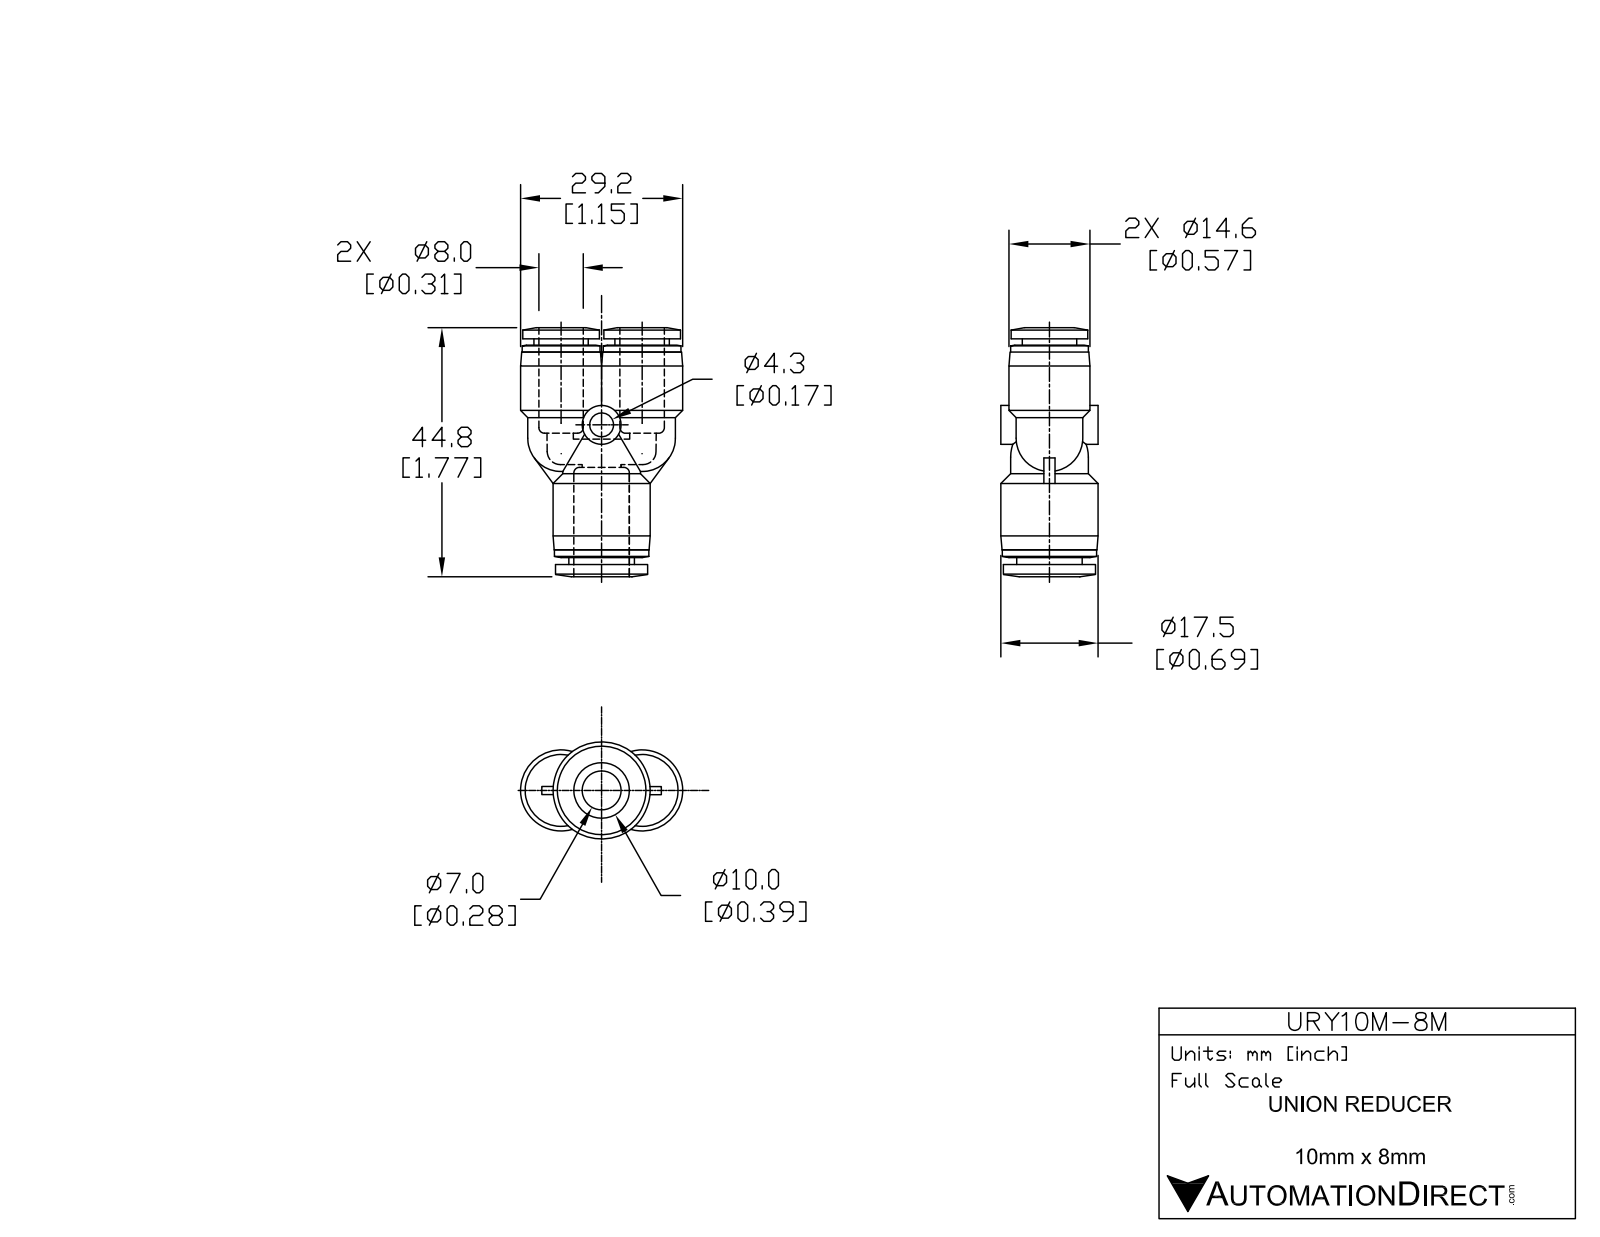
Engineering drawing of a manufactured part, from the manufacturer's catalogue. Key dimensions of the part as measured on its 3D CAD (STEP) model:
Part name (STEP PRODUCT): URY10M-8M
STEP written by: SolidWorks 2015 (AUTOMOTIVE_DESIGN)
Units: inches
Bodies: 1 solid, 110 faces (21 planar, 44 cylindrical, 45 other)
Overall size (bounding box): 1.75 × 1.15 × 0.689
Volume: 0.47 in³ · Surface area: 9.701 in²
Round holes (diameter × count): ⌀0.327 ×2, ⌀0.169 ×1, ⌀0.406 ×1
Round bosses / shafts (diameter × count): ⌀0.551 ×3, ⌀0.575 ×2, ⌀0.543 ×2, ⌀0.386 ×2, ⌀0.689 ×1, ⌀0.669 ×1, ⌀0.654 ×1, ⌀0.465 ×1
Partial cylindrical surfaces — rounded edges, fillets, slot ends (radius × count): R0.236 ×2
Main face-to-face distances: 1.585, 1.539, 0.045, 0.931, 0.608, 0.654, 0.049, 1.49, 0.693, 0.238
Hole centre spacings: 0.287, 0.575
